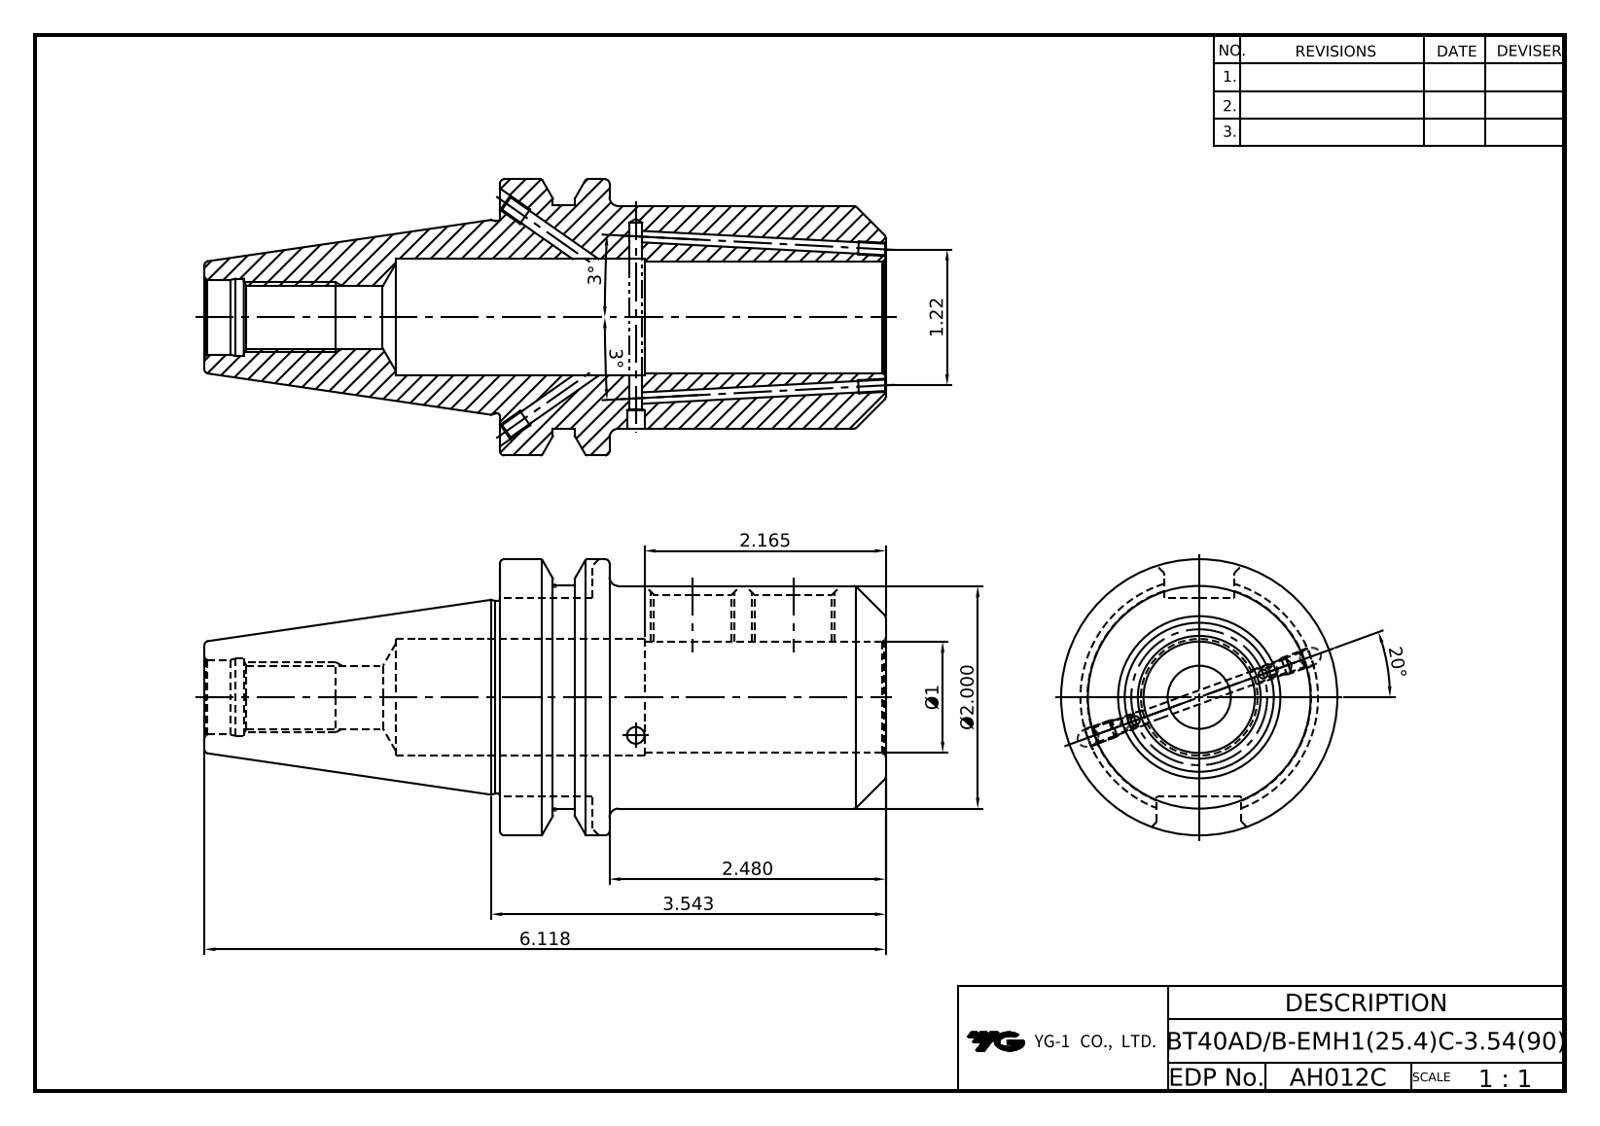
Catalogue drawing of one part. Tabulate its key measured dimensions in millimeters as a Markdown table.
| quantity | value |
| --- | --- |
| part name | BT40ADB_EMH25_4C_90 |
| STEP written by | CREO PARAMETRIC BY PTC INC, 2018100 (CONFIG_CONTROL_DESIGN) |
| units | millimeters |
| bodies | 1 solid, 156 faces (34 planar, 74 cylindrical, 48 other) |
| overall size | 155.4 × 63 × 63 |
| volume | 180 717 mm³ |
| surface area | 44 614 mm² |
| round holes (diameter × count) | 4 × 7, 3.4 × 4, 3 × 3, 2.5 × 2, 17.46 × 2, 19.05 × 2, 14 × 1, 16 × 1, 17 × 1, 17.6 × 1, 25.4 × 1, 26.6 × 1 |
| round bosses / shafts (diameter × count) | 63 × 1, 51 × 1, 50.8 × 1, 44 × 1 |
| partial cylindrical surfaces (radius × count) | 8.05 × 1 |
| main face-to-face distances | 25, 88, 63, 45.2, 17.1, 7.9, 70.9, 12.1, 5, 12.9 |
| hole center spacings | 29.89, 29.9, 22.9 |
